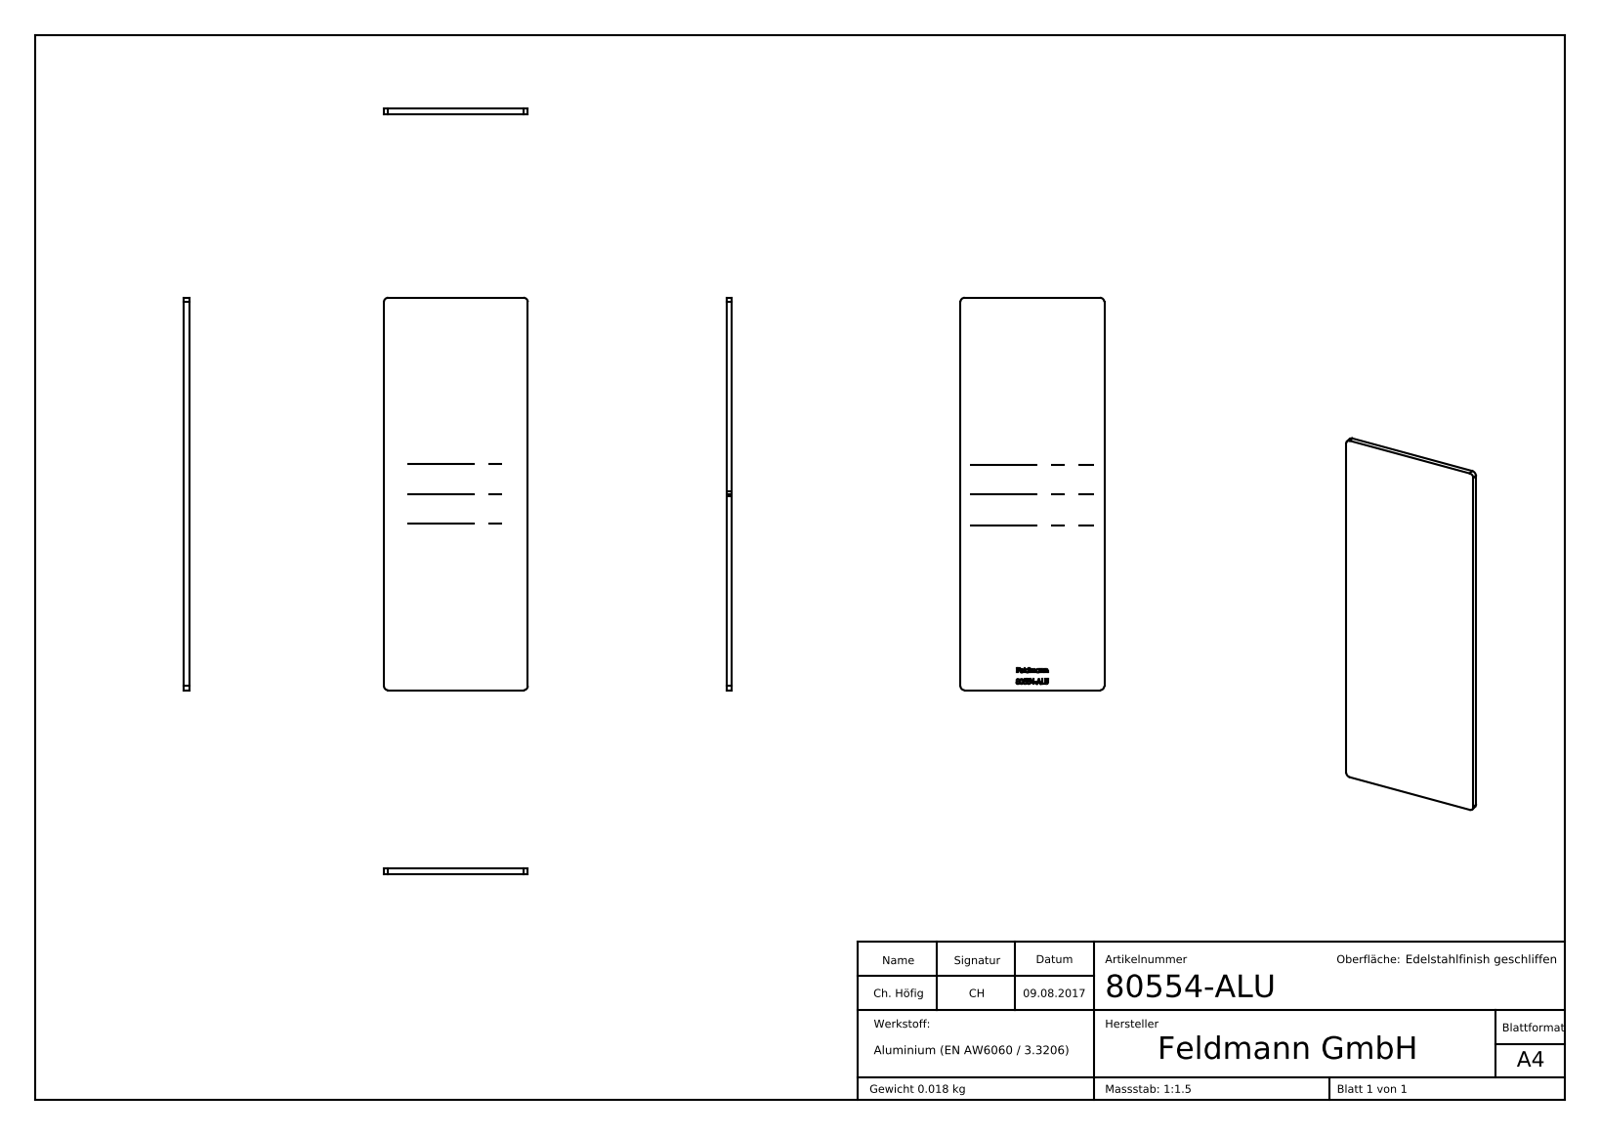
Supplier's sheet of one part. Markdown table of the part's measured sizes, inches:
| quantity | value |
| --- | --- |
| part name | 80554-ALU |
| STEP written by | SolidWorks 2015 (CONFIG_CONTROL_DESIGN) |
| units | inches |
| bodies | 1 solid, 238 faces (137 planar, 4 cylindrical, 97 other) |
| overall size | 4.35 × 1.594 × 0.059 |
| volume | 0.409 in³ |
| surface area | 14.58 in² |
| partial cylindrical surfaces (radius × count) | 0.047 × 4 |
| main face-to-face distances | 0.059, 1.594, 4.35, 0.055, 0.029, 0.146, 0.052, 0.275, 0.129, 0.161 |
